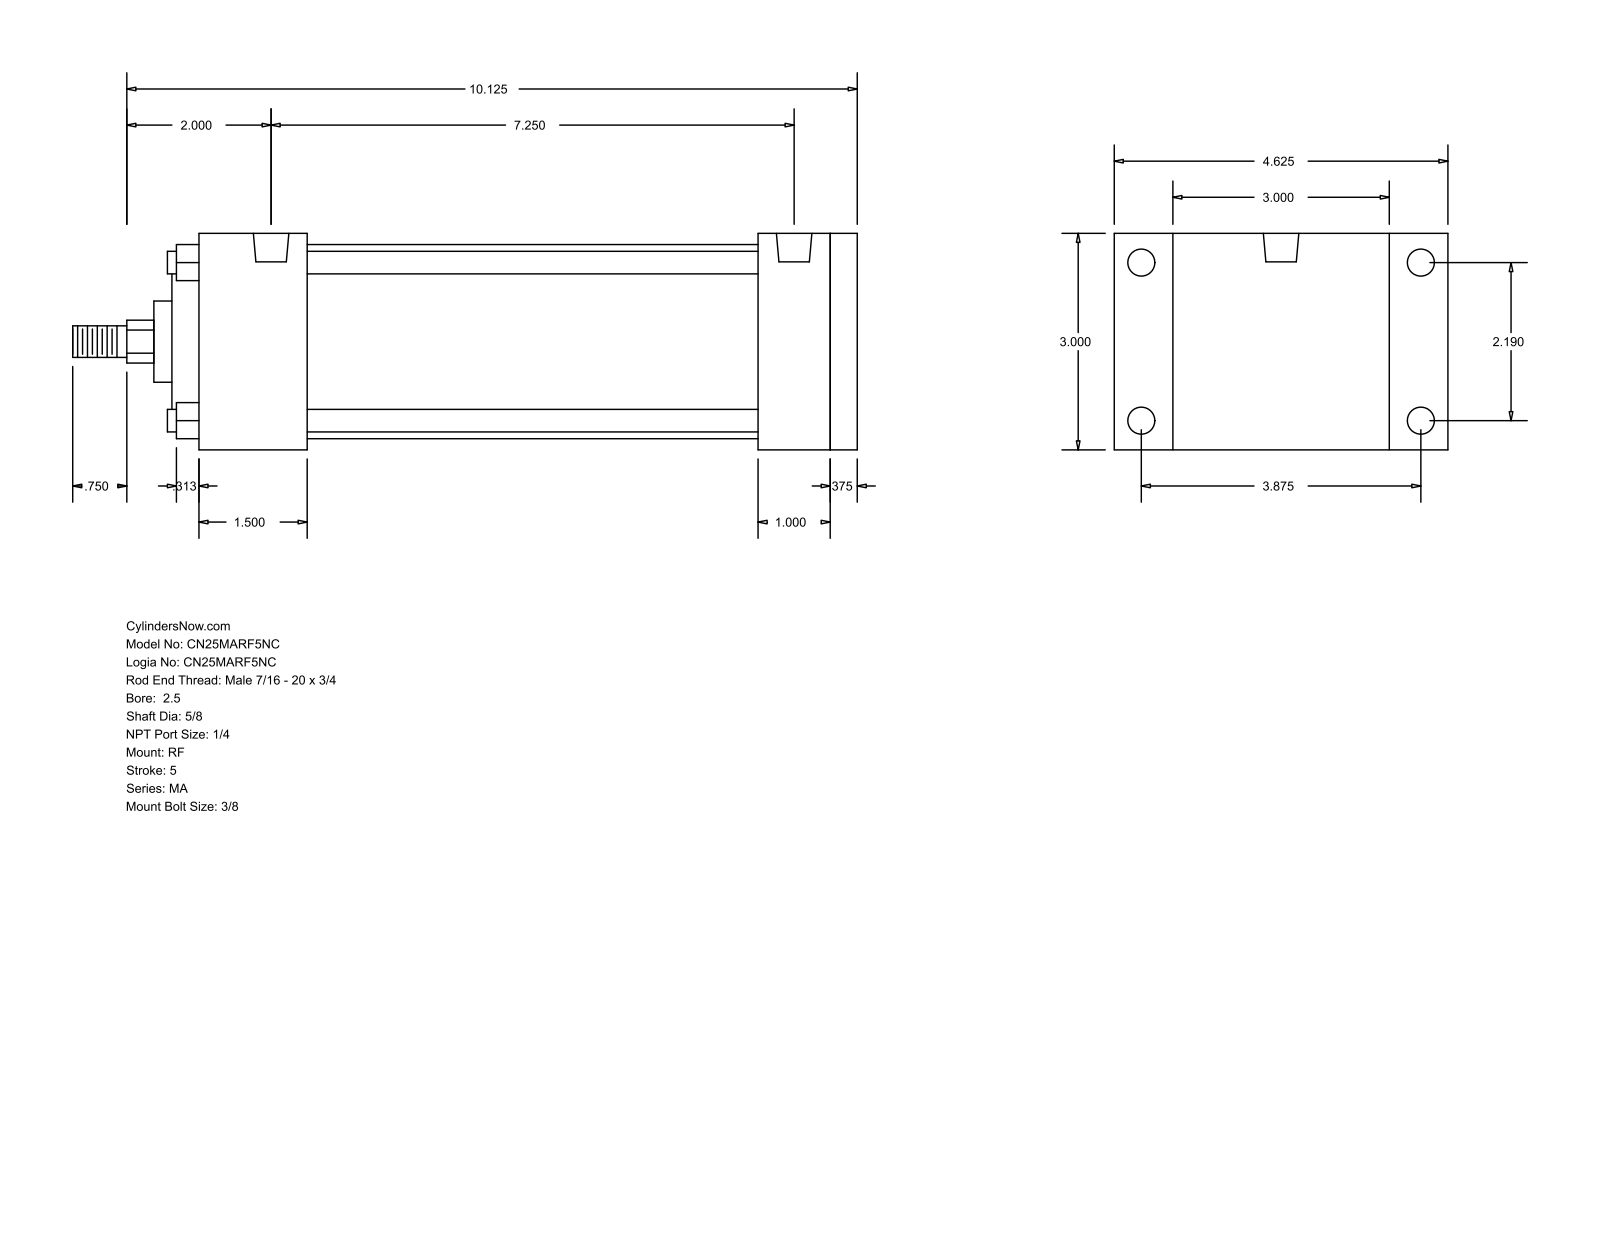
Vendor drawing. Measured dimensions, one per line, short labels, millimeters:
name: MA_RF__0250_0.625
written by: GSSL Pune (CONFIG_CONTROL_DESIGN)
unit: mm
bodies: 0 solids, 94 faces (65 planar, 29 cylindrical, 0 other)
size: 276.23 × 117.47 × 76.2
holes: 4× ⌀7.94, 4× ⌀9.53, 2× ⌀12.49
bosses: 4× ⌀7.94, 1× ⌀68.33, 1× ⌀50.8, 1× ⌀28.57, 1× ⌀15.88, 1× ⌀11.11
rounds: 1× R7.54
face distances: 76.2, 231.78, 9.53, 222.25, 25.4, 34.93, 38.1, 196.85, 158.75, 184.15
hole spacings: 55.62, 98.42, 113.05, 184.15
